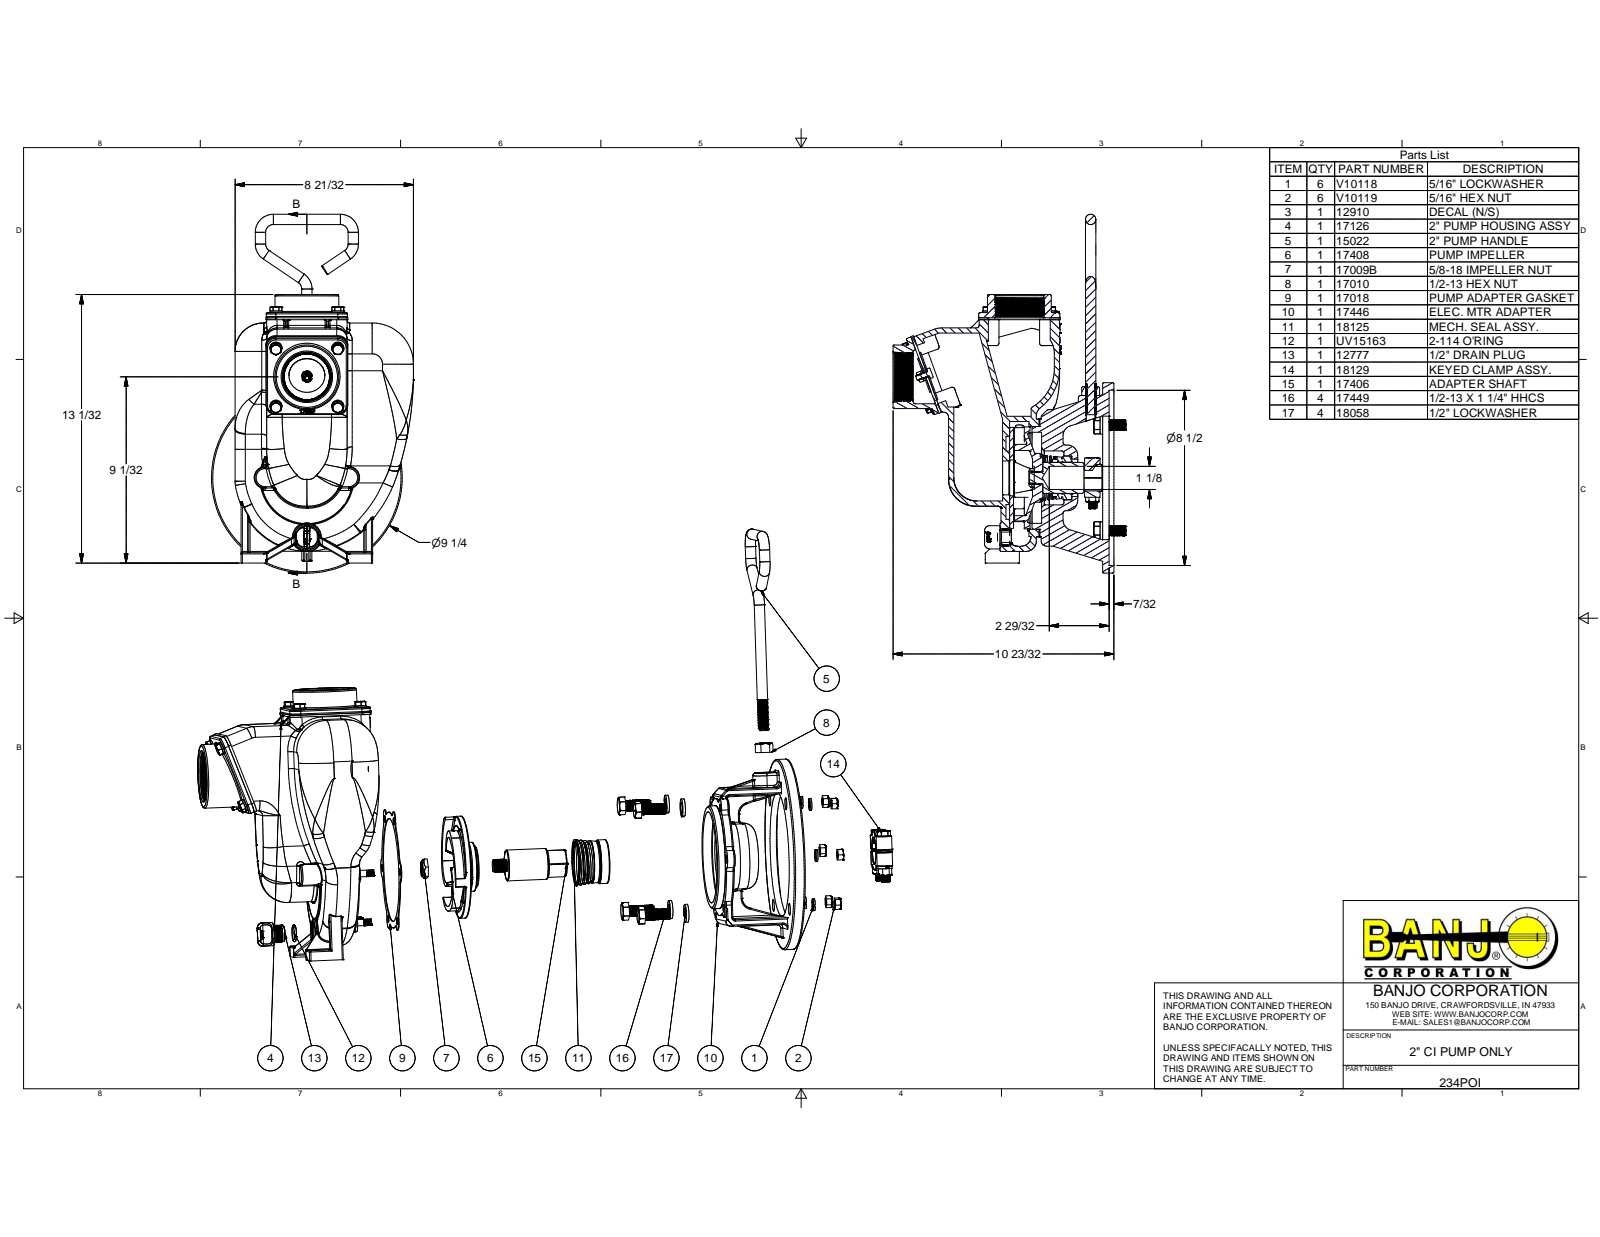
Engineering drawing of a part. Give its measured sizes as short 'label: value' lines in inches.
name: 234POI; 17126; 17026; 17000 (+8 more)
written by: Autodesk Inventor 2013 (AUTOMOTIVE_DESIGN)
unit: in
bodies: 79 solids, 5838 faces (1089 planar, 2023 cylindrical, 2726 other)
size: 17.429 × 11.295 × 9.798
volume: 165.4 in³; area: 1 354 in²
holes: 17× ⌀0.252, 14× ⌀0.322, 8× ⌀0.313, 8× ⌀0.343, 6× ⌀0.252, 6× ⌀0.375, 4× ⌀0.512, 4× ⌀0.562, 2× ⌀0.196, 2× ⌀0.25, 2× ⌀0.307, 2× ⌀0.385
bosses: 132× ⌀0.268, 60× ⌀0.436, 30× ⌀0.324, 14× ⌀0.583, 12× ⌀0.212, 10× ⌀0.313, 9× ⌀0.5, 6× ⌀0.246
rounds: 84× R0.06, 62× R0.03, 50× R0.25, 33× R0.125, 29× R0.09, 24× R0.5, 16× R0.063, 16× R0.469
face distances: 0.25, 0.31, 4.516, 4.826, 3.65, 0.125, 0.337, 4.853, 5.163, 0.193
hole spacings: 3, 2.121, 2.813, 2.122, 4.243, 4.243, 4.872, 1.164
